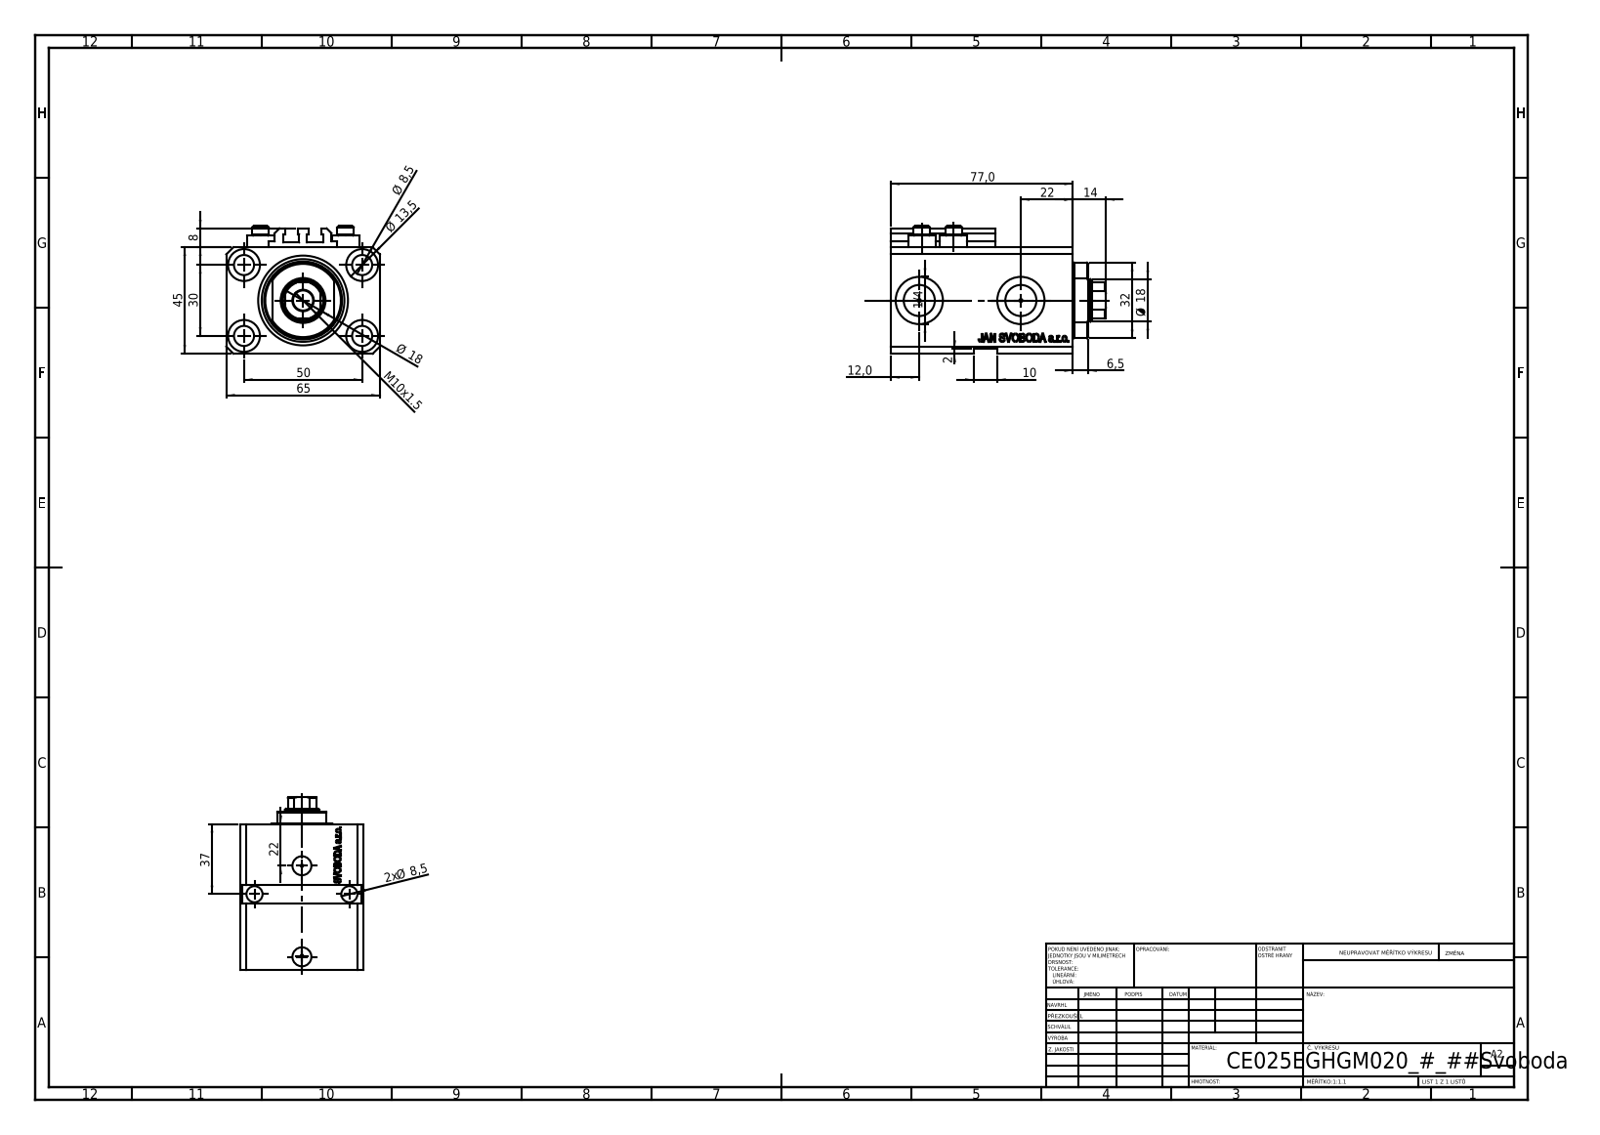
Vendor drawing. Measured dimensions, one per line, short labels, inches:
name: V250CE_VC_E; V250CE_C_VCP; V250CE_E_Body; ALLEN BOLT V250CE
written by: SolidWorks 2019 (CONFIG_CONTROL_DESIGN)
unit: in
bodies: 8 solids, 1067 faces (511 planar, 126 cylindrical, 430 other)
size: 3.583 × 2.559 × 2.126
volume: 12.19 in³; area: 91.74 in²
holes: 7× ⌀0.335, 4× ⌀0.049, 4× ⌀0.157, 4× ⌀0.531, 2× ⌀0.394, 2× ⌀0.518, 2× ⌀0.787, 1× ⌀0.709, 1× ⌀0.984, 1× ⌀1.496
bosses: 4× ⌀0.457, 4× ⌀0.276
rounds: 10× R0.008, 1× R0.335, 1× R0.63
face distances: 1.772, 2.559, 2.48, 0.551, 3.031, 0.079, 0.272, 2.209, 2.76, 1.85
hole spacings: 1.148, 1.969, 0.535, 0.595, 0.741, 0.747, 1.032, 1.048
